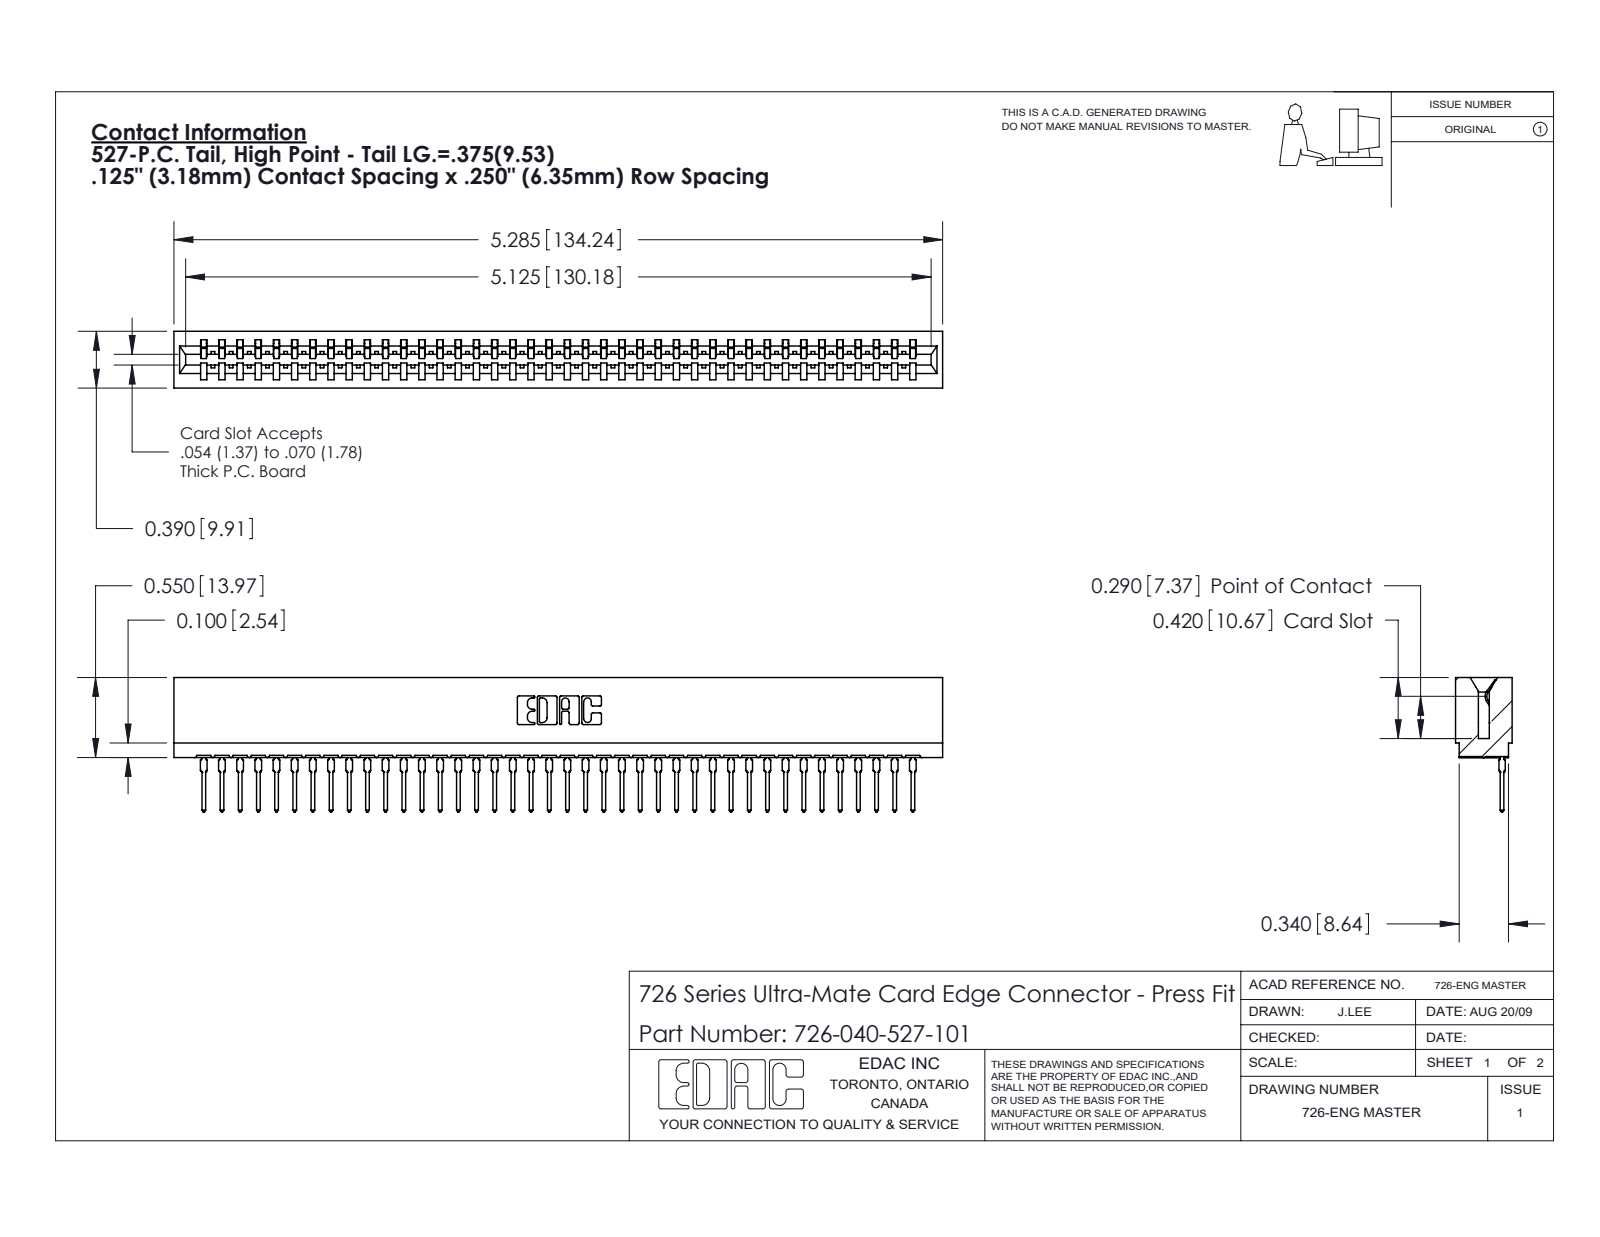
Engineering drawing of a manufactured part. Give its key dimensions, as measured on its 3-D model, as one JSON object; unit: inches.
{"part_name": "726-040-527-101; 746-292-001_527; 726 Part_.515 Slot Depth - 01", "step_written_by": "SolidWorks 2020 (CONFIG_CONTROL_DESIGN)", "units": "inches", "bodies": {"solids": 41, "faces": 4417, "planar": 2575, "cylindrical": 802, "other": 1040}, "overall_size": [5.285, 0.924, 0.39], "volume_in3": 0.734, "surface_area_in2": 28.78, "partial_cylinders_radius": [[0.021, 80], [0.015, 41], [0.01, 22], [0.007, 6], [0.031, 6], [0.005, 4], [0.011, 4], [0.026, 3]], "face_to_face_distances": [0.057, 0.333, 0.39, 0.25, 0.025, 0.307, 0.083, 0.275, 0.365, 0.032]}
